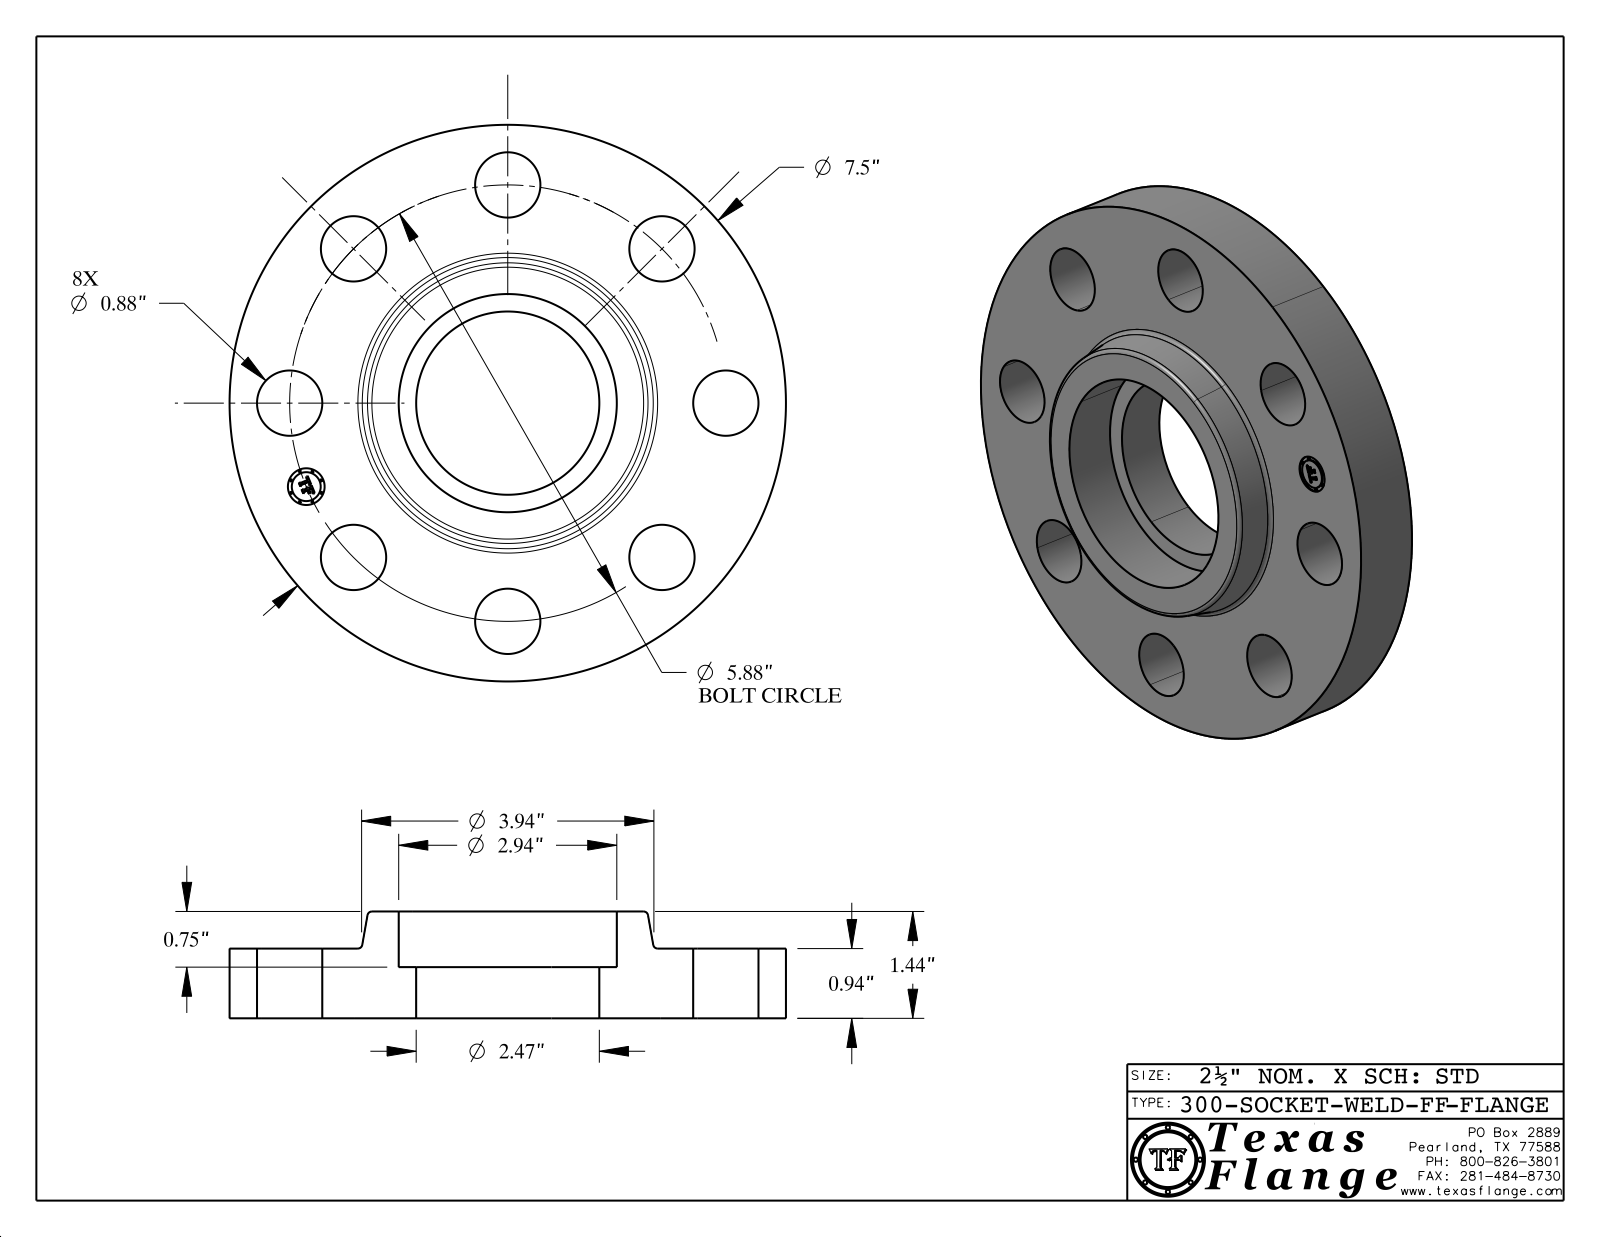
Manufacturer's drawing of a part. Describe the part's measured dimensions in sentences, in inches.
The part is named "300-SOCKET-WELD-FF". Its 3-D file was written by "CATIA V5 STEP AP214 (AUTOMOTIVE_DESIGN)". It is 1 solid with 418 faces: 370 planar, 42 cylindrical and 6 other. Overall it measures 7.5 by 7.5 by 1.44 inches. Its volume is 34.39 cubic inches and its surface area 129 square inches. Round holes: 8 of diameter 0.88, 1 of diameter 0.495, 1 of diameter 2.469, 1 of diameter 2.94. Round bosses or shafts: 8 of diameter 0.03, 1 of diameter 7.5, 1 of diameter 0.39. The main face-to-face distances are 0.94, 1.44, 0.5, 0.69, 0.25, 0.75, 0.015, 0.925, 0.235, 0.515. The hole center spacings are 2.25, 5.432, 2.94, 2.94, 4.157, 4.158, 3.267, 5.88.
